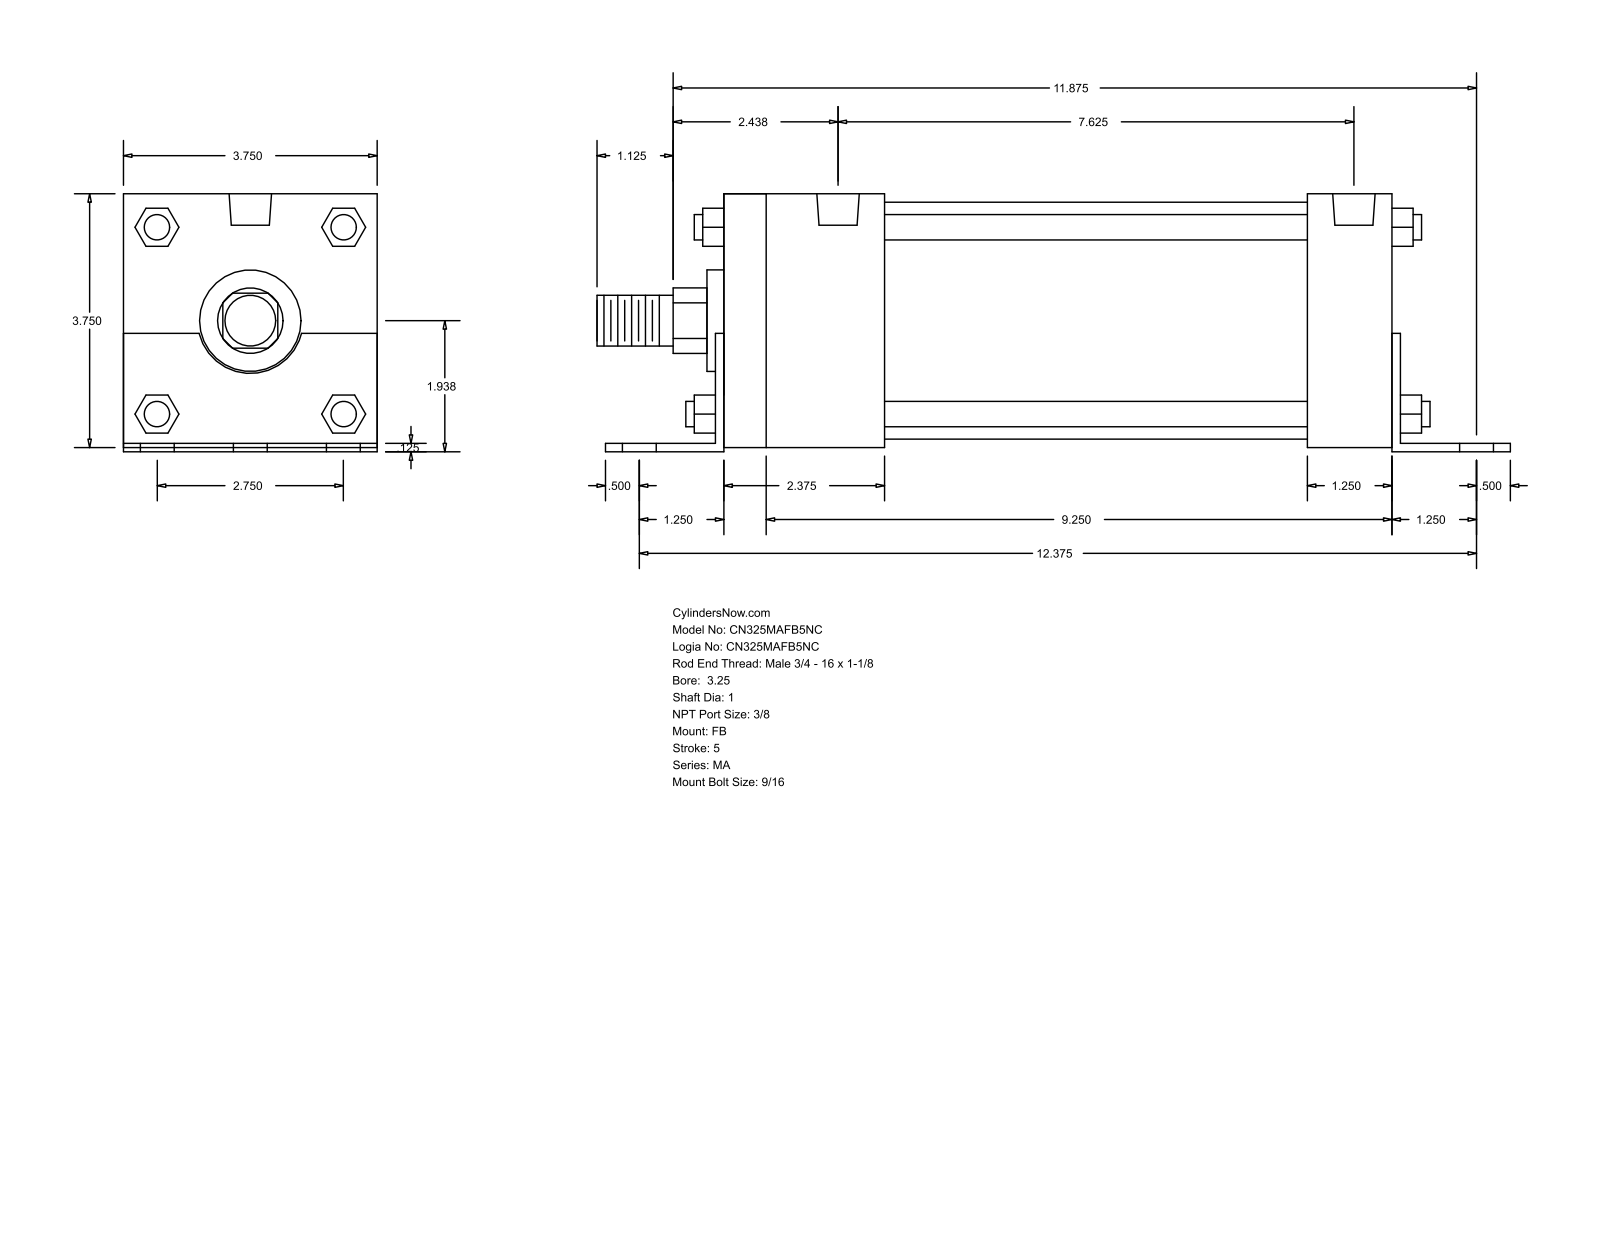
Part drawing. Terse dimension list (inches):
name: MA_FB__0325_1
written by: GSSL Pune (CONFIG_CONTROL_DESIGN)
unit: in
bodies: 0 solids, 140 faces (105 planar, 35 cylindrical, 0 other)
size: 13.5 × 3.813 × 3.75
holes: 6× ⌀0.563, 4× ⌀0.437, 2× ⌀0.627
bosses: 4× ⌀0.375, 1× ⌀3.5, 1× ⌀1.5, 1× ⌀1, 1× ⌀0.75
rounds: 1× R0.484, 1× R0.78
face distances: 3.75, 0.125, 0.063, 3.812, 0.062, 3.687, 10, 9.875, 10.125, 1.375
hole spacings: 1.375, 12.451, 12.375, 2.275, 2.427, 2.75, 3.243, 3.414
